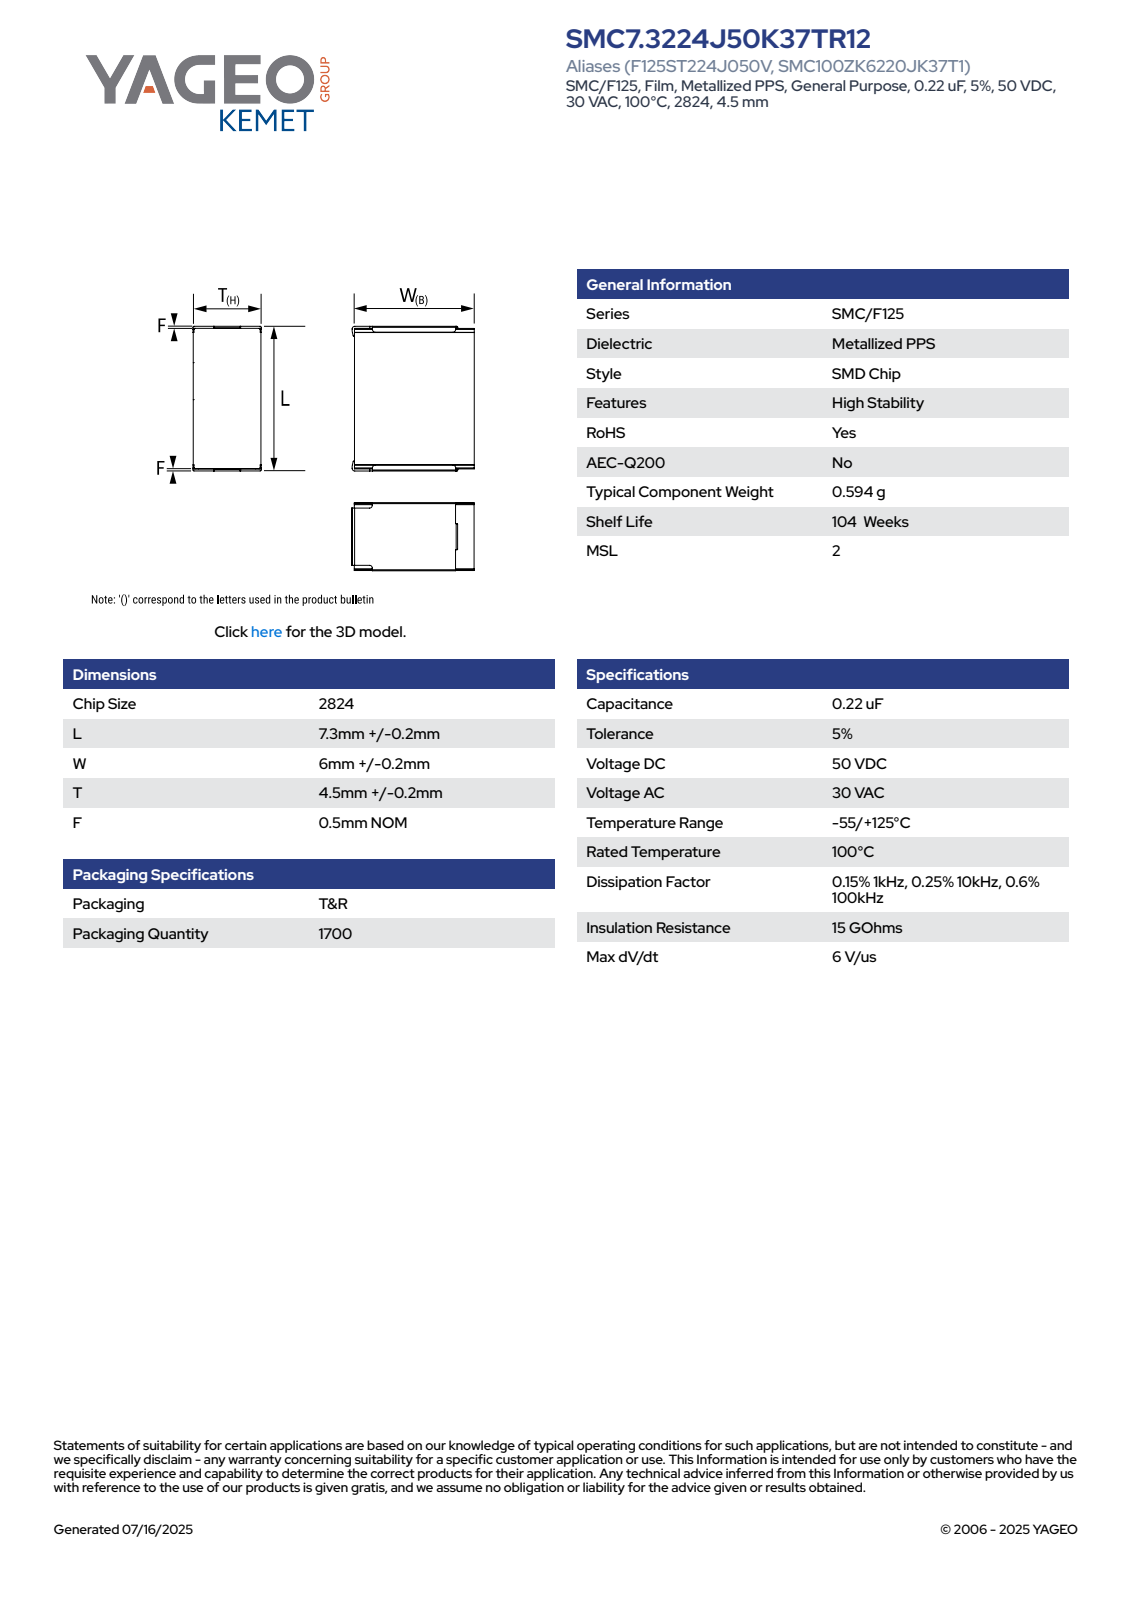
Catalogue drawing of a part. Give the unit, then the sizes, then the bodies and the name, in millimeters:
Units: millimetres
Overall size (bounding box): 7.5 × 6.41 × 4.94
Partial cylindrical surfaces — rounded edges, fillets, slot ends (radius × count): R0.28 ×10, R0.26 ×4
Main face-to-face distances: 4.7, 5.95, 7.5, 0.5, 7, 4.82, 6.5, 4.94, 6.41, 0.46
Volume: 207 mm³ · Surface area: 231 mm²
Bodies: 4 solids, 121 faces (107 planar, 14 cylindrical, 0 other)
Part name (STEP PRODUCT): CFS_KSTD_2824_L7.5W6.2T4.7F0.5
STEP written by: SolidWorks 2021 (AUTOMOTIVE_DESIGN)
